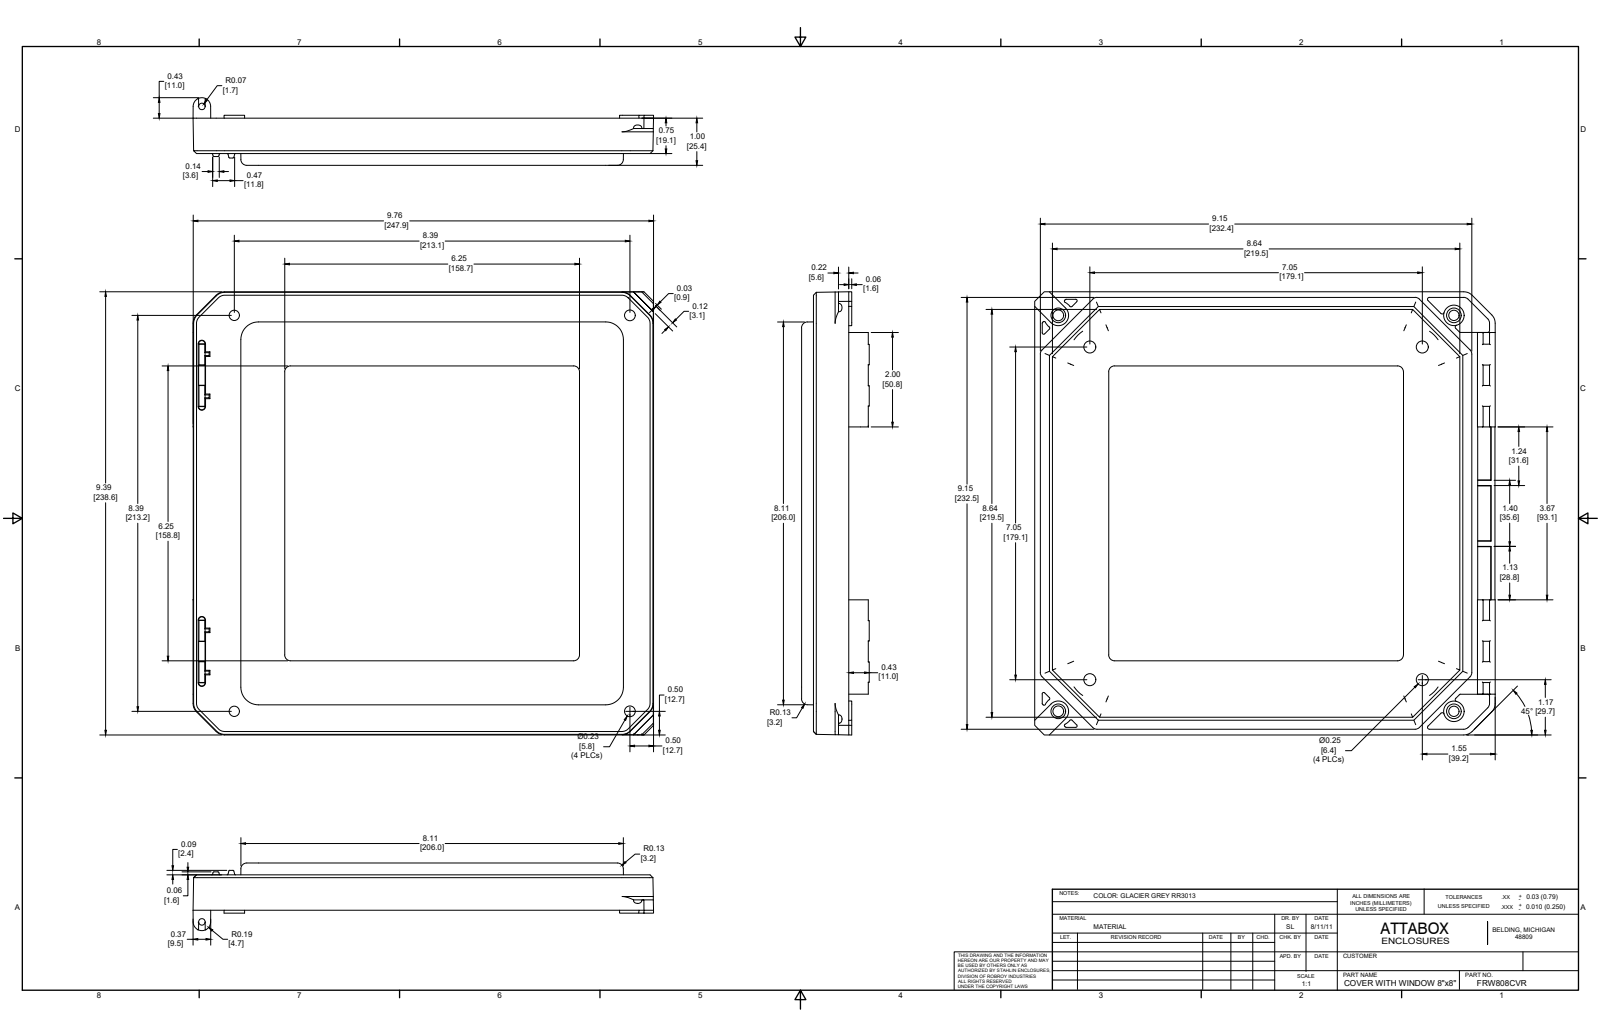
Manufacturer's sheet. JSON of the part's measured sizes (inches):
{"part_name": "FRW808CVR", "step_written_by": "SolidWorks 2019 (AUTOMOTIVE_DESIGN)", "units": "inches", "bodies": {"solids": 1, "faces": 589, "planar": 245, "cylindrical": 196, "other": 148}, "overall_size": [9.765, 9.392, 1.434], "volume_in3": 17.43, "surface_area_in2": 195.9, "round_holes": [[0.253, 4], [0.219, 2], [0.227, 2], [0.313, 2], [0.137, 1]], "round_bosses_or_shafts": [[0.435, 2]], "partial_cylinders_radius": [[0.03, 27], [0.096, 16], [0.125, 16], [0.01, 14], [0.062, 12], [0.063, 12], [0.04, 10], [0.06, 9]], "face_to_face_distances": [0.25, 0.125, 0.125, 0.375, 0.75, 1, 0.625, 0.875, 0.375, 0.625], "hole_center_spacings": [7.751, 0.947, 0.948, 7.051, 7.051, 7.749, 7.75, 8.39]}
